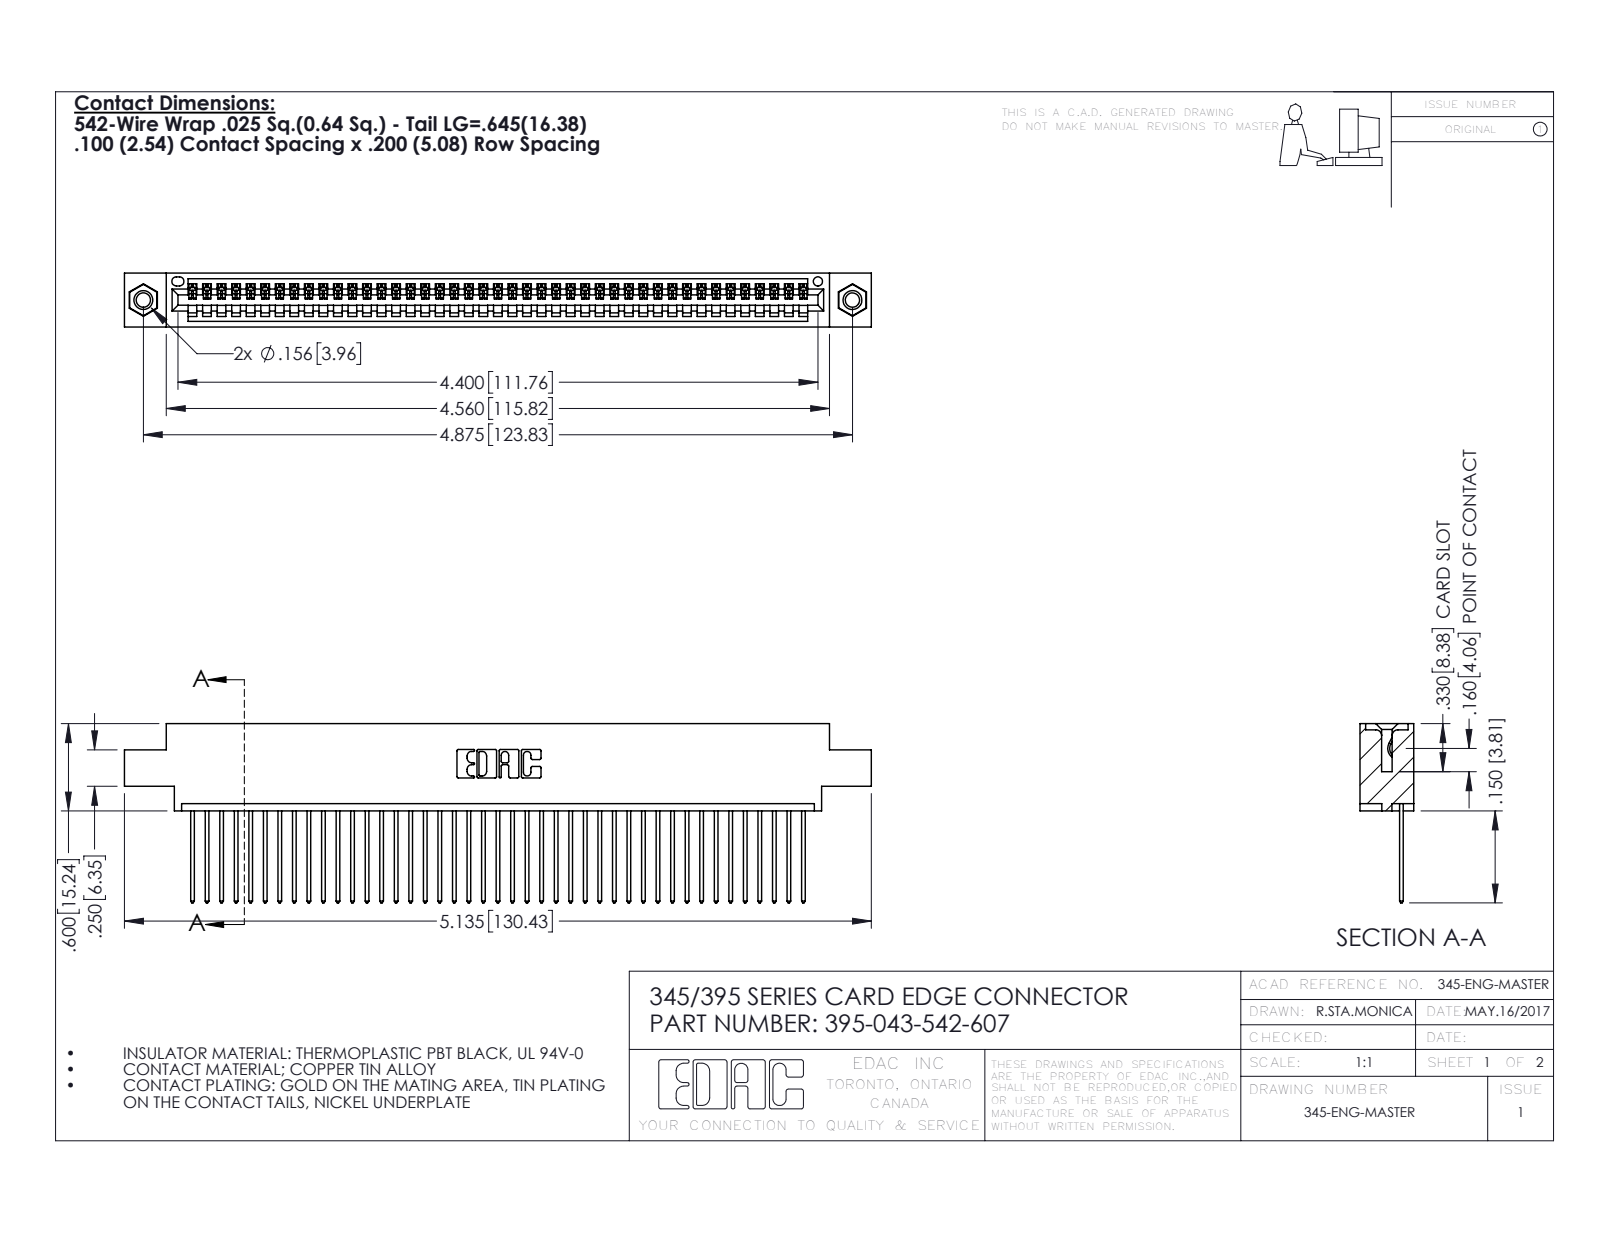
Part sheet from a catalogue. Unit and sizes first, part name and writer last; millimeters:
Units: millimetres
Overall size (bounding box): 130.4 × 31.3 × 9.4
Round holes (diameter × count): ⌀2.5 ×2, ⌀3.2 ×2, ⌀4 ×2, ⌀1.6 ×1
Round bosses / shafts (diameter × count): ⌀3.9 ×2
Partial cylindrical surfaces — rounded edges, fillets, slot ends (radius × count): R0.2 ×86, R0.3 ×86, R0.3 ×22, R0.2 ×6, R0.8 ×6, R0.7 ×3, R0.8 ×2, R1 ×2
Main face-to-face distances: 1.8, 7.6, 9.4, 2.5, 6.9, 0.6, 5.1, 5.7, 4.4, 3.8
Hole centre spacings: 6.9, 117.8, 123.8
Volume: 12 400 mm³ · Surface area: 17 210 mm²
Bodies: 46 solids, 2684 faces (1836 planar, 832 cylindrical, 16 other)
Part name (STEP PRODUCT): 345-292-001_345-293-142; 395-043-542-607; 345-250-001_345-250-005-103; 345 Part_0.170 Offset - 0.156 Dia-TI
STEP written by: SolidWorks 2016 (CONFIG_CONTROL_DESIGN)
